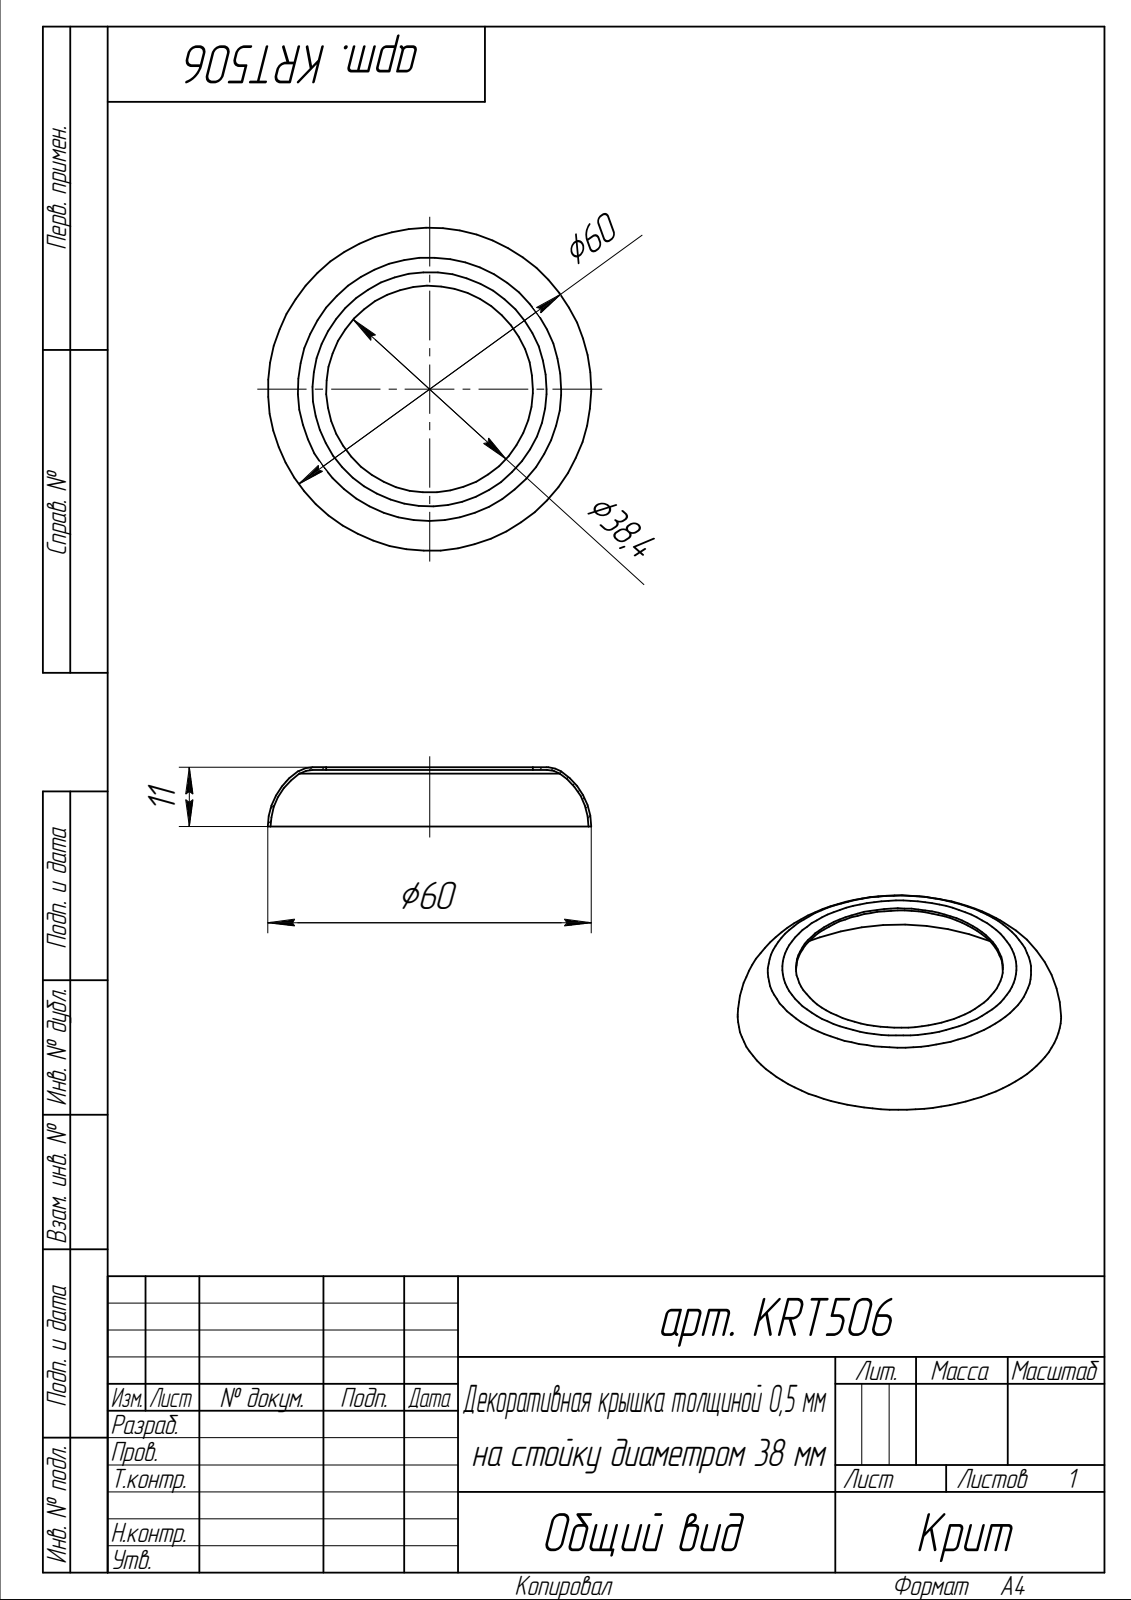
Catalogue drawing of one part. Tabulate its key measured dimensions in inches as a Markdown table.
| quantity | value |
| --- | --- |
| part name | арт. KRT506 |
| STEP written by | SolidWorks 2014 (AUTOMOTIVE_DESIGN) |
| units | inches |
| bodies | 1 solid, 13 faces (3 planar, 2 cylindrical, 8 other) |
| overall size | 2.362 × 2.362 × 0.433 |
| volume | 0.085 in³ |
| surface area | 8.913 in² |
| round holes (diameter × count) | 1.512 × 1 |
| main face-to-face distances | 0.02, 0.413, 0.433 |
